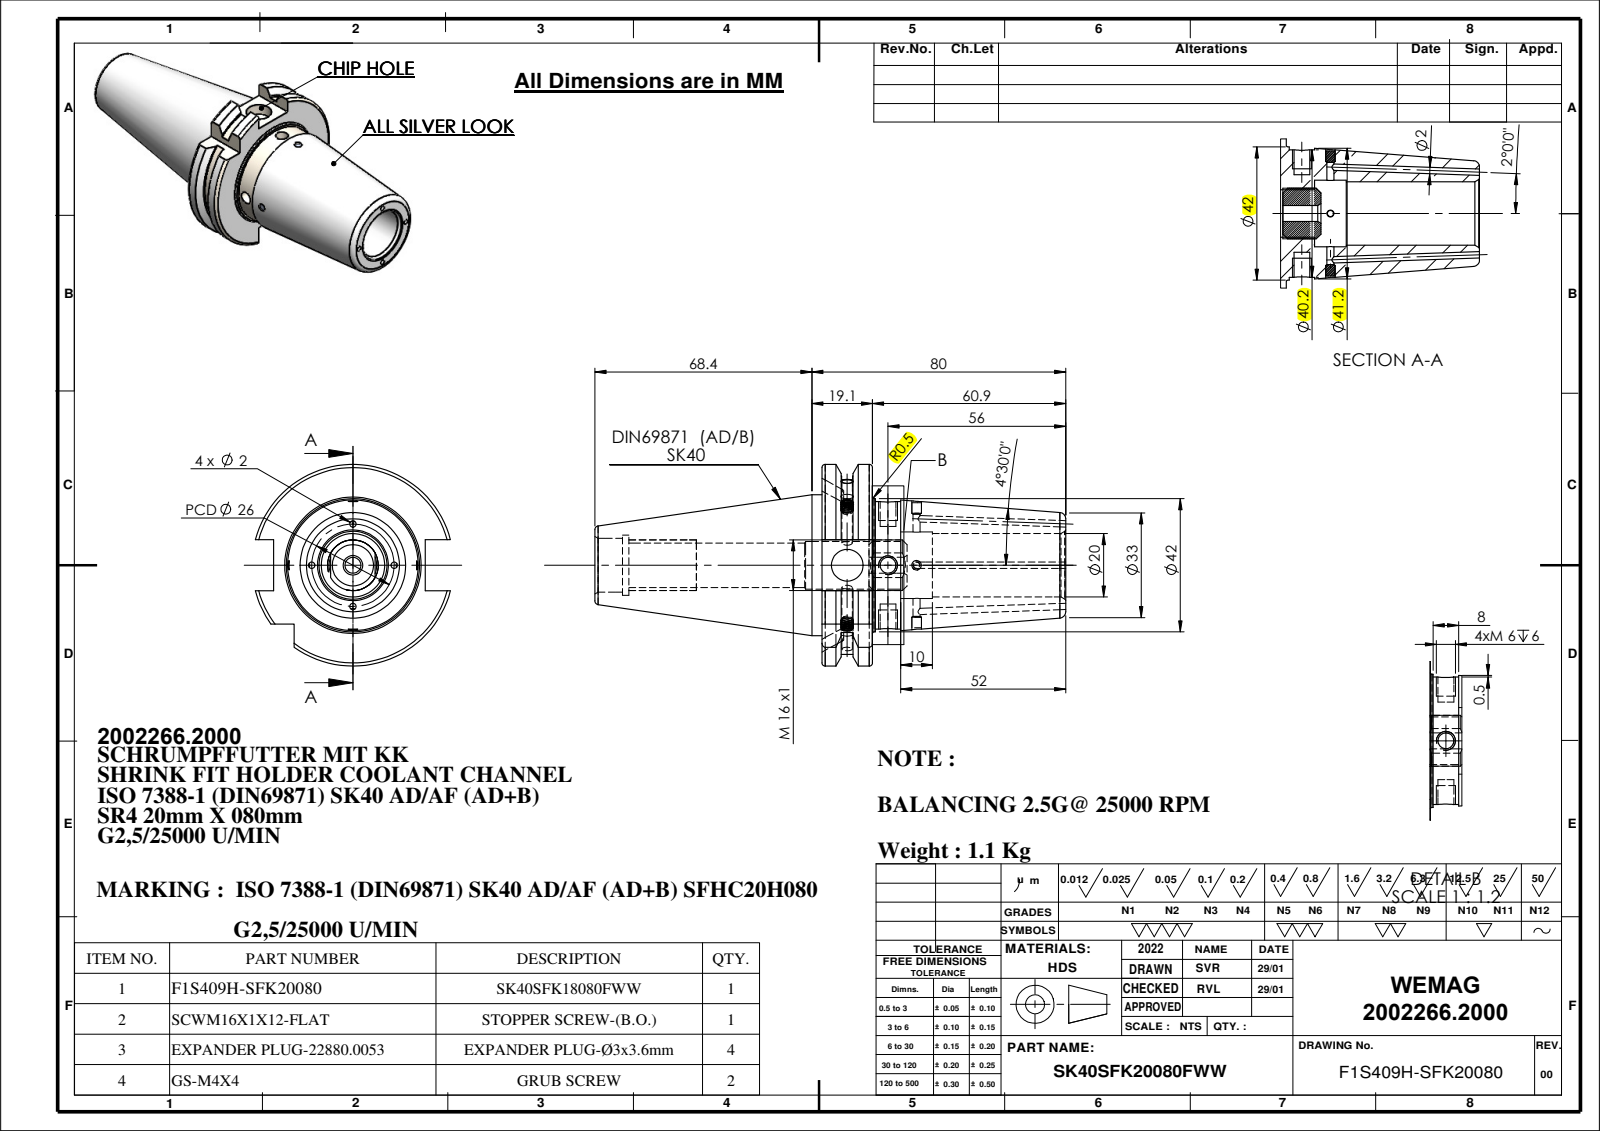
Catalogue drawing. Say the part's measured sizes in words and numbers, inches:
The part is named "GS-M4X4_DIN 913 - M4 x 4-N; SCWM16X1X12-FLAT; SK40SFK20080FWW; EXPANDER PLUG Ø3x3.6 (+1 more)". Its 3-D file was written by "SolidWorks 2018 (CONFIG_CONTROL_DESIGN)". It is 8 solids with 267 faces: 60 planar, 91 cylindrical and 116 other. Overall it measures 5.843 by 2.502 by 2.42 inches. Its volume is 9.123 cubic inches and its surface area 53.41 square inches. Round holes: 4 of diameter 0.079, 2 of diameter 0.087, 2 of diameter 0.118, 1 of diameter 0.13, 1 of diameter 0.197, 1 of diameter 0.394, 1 of diameter 0.551, 1 of diameter 0.591, 1 of diameter 0.669, 1 of diameter 0.748, 1 of diameter 0.787, 1 of diameter 0.826. Round bosses or shafts: 2 of diameter 0.157, 1 of diameter 1.75, 1 of diameter 1.654. Partial cylindrical surfaces (rounded edges, fillets, slot ends): 1 of radius 0.315, 1 of radius 1.107, 1 of radius 1.251. The main face-to-face distances are 0.626, 2.398, 3.024, 0.634, 1.882, 0.079, 0.976, 0.35, 2.047, 3.453. The hole center spacings are 0.86.
